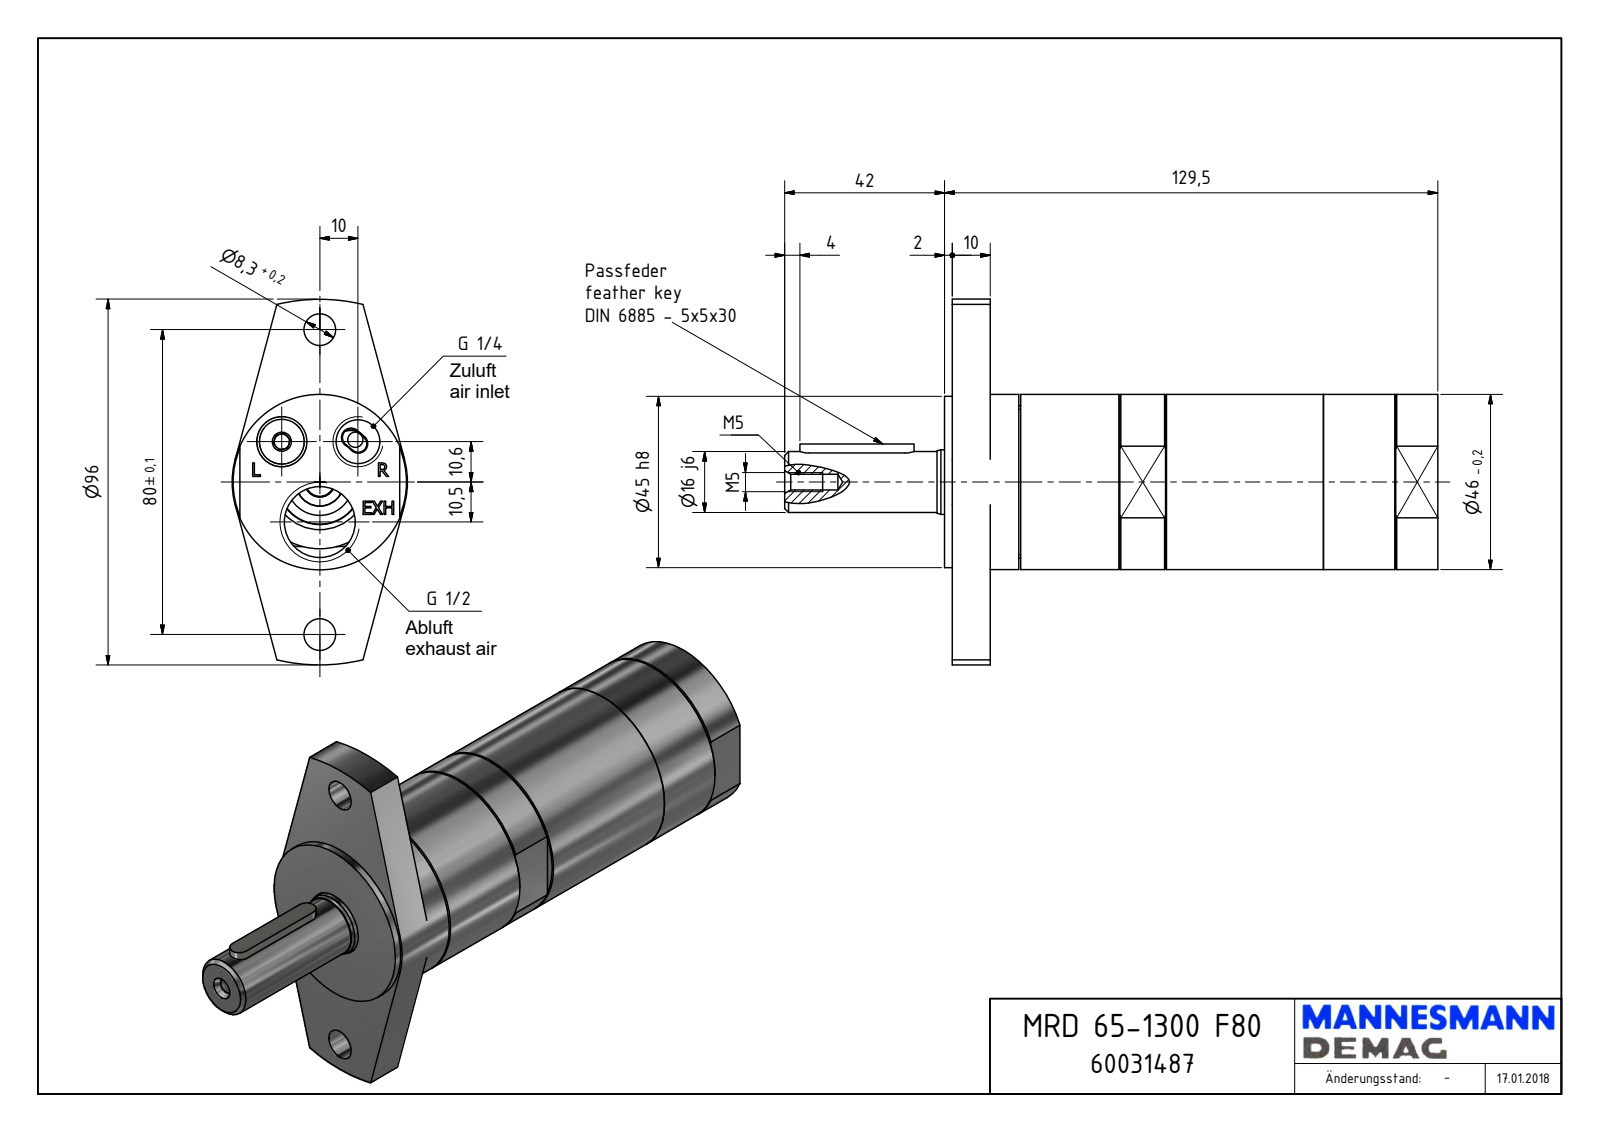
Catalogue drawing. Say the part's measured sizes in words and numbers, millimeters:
The part is named "MRD 65-1300 F80_60031487". Its 3-D file was written by "Autodesk Inventor 2018 (AUTOMOTIVE_DESIGN)". It is 1 solid with 165 faces: 108 planar, 31 cylindrical and 26 other. Overall it measures 171.5 by 96 by 46 millimeters. Its volume is 233 883 cubic millimeters and its surface area 31 801 square millimeters. Round holes: 2 of diameter 8.3, 1 of diameter 4, 1 of diameter 4.13, 1 of diameter 11.45, 1 of diameter 17.5, 1 of diameter 18.63. Round bosses or shafts: 1 of diameter 46, 1 of diameter 45, 1 of diameter 40, 1 of diameter 32.86, 1 of diameter 16.95, 1 of diameter 16. Partial cylindrical surfaces (rounded edges, fillets, slot ends): 2 of radius 2.5, 2 of radius 5, 1 of radius 5.72, 1 of radius 19, 1 of radius 48. The main face-to-face distances are 10, 2, 12, 117.5, 129.5, 127.5, 42, 8, 109.5, 46. The hole center spacings are 14.57, 23.35, 31.05, 40, 51.58, 10.5, 20, 29.5.
